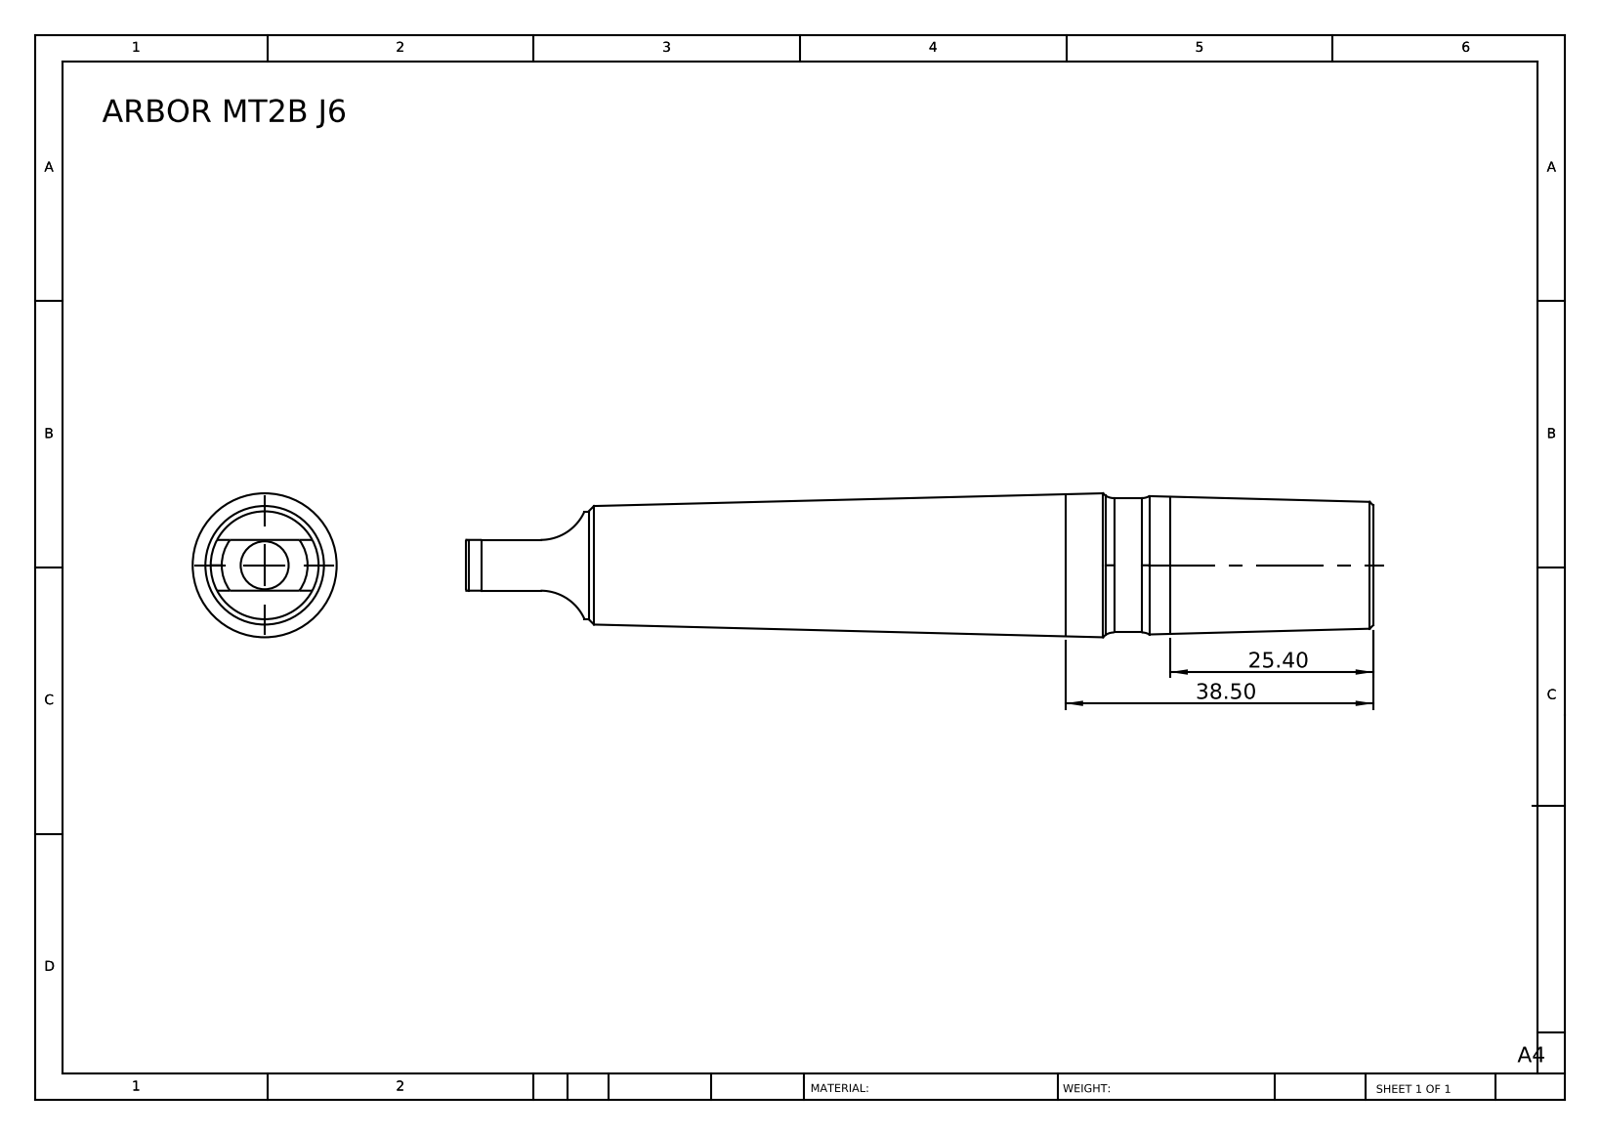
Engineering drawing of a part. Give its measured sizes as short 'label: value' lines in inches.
name: ARBOR MT2B J6
written by: SolidWorks 2014 (CONFIG_CONTROL_DESIGN)
unit: in
bodies: 1 solid, 29 faces (4 planar, 6 cylindrical, 19 other)
size: 4.469 × 0.709 × 0.709
volume: 1.366 in³; area: 9.236 in²
bosses: 1× ⌀0.661, 1× ⌀0.531
rounds: 2× R0.236
face distances: 0.25, 4.469
